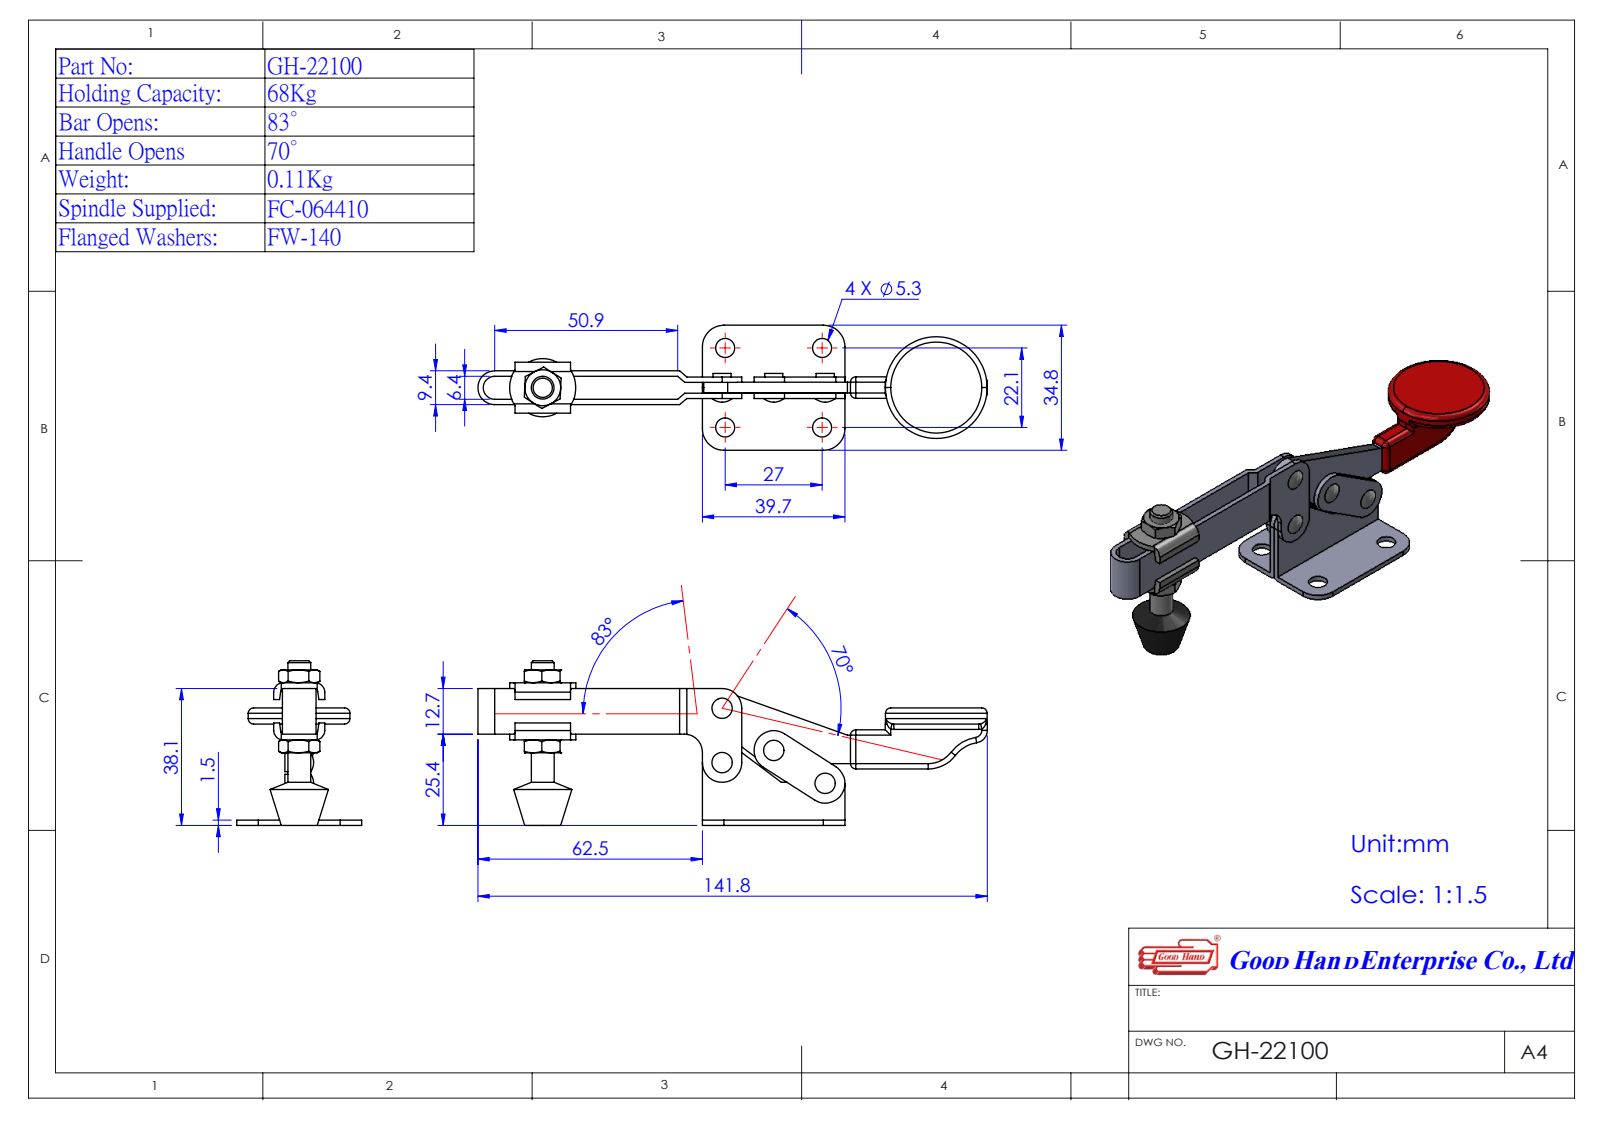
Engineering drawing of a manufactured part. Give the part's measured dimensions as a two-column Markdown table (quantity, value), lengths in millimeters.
| quantity | value |
| --- | --- |
| part name | GH-22100(簡化); Group5^GH-22100(簡化); Group3^GH-22100(簡化); 12210001-1^GH-22100(簡化) (+2 more) |
| STEP written by | SolidWorks 2016 (AUTOMOTIVE_DESIGN) |
| units | millimeters |
| bodies | 5 solids, 264 faces (118 planar, 100 cylindrical, 46 other) |
| overall size | 142.12 × 45.8 × 34.8 |
| volume | 18 387 mm³ |
| surface area | 17 651 mm² |
| round holes (diameter × count) | 3 × 4, 5.3 × 4, 5 × 1, 6 × 1, 6.3 × 1 |
| round bosses / shafts (diameter × count) | 4.05 × 2, 4 × 2, 28.32 × 1, 11 × 1, 6.35 × 1, 3 × 1 |
| partial cylindrical surfaces (radius × count) | 1 × 4, 2.6 × 4, 6 × 4, 5.5 × 3, 5 × 2, 3.2 × 1, 3.5 × 1, 4.5 × 1 |
| main face-to-face distances | 1.5, 1.7, 6.2, 4.5, 3, 4.7, 7.7, 3.2, 7.9, 6 |
| hole center spacings | 22.1, 27, 34.89, 51.99, 78.58, 14.91, 15.1, 17 |
